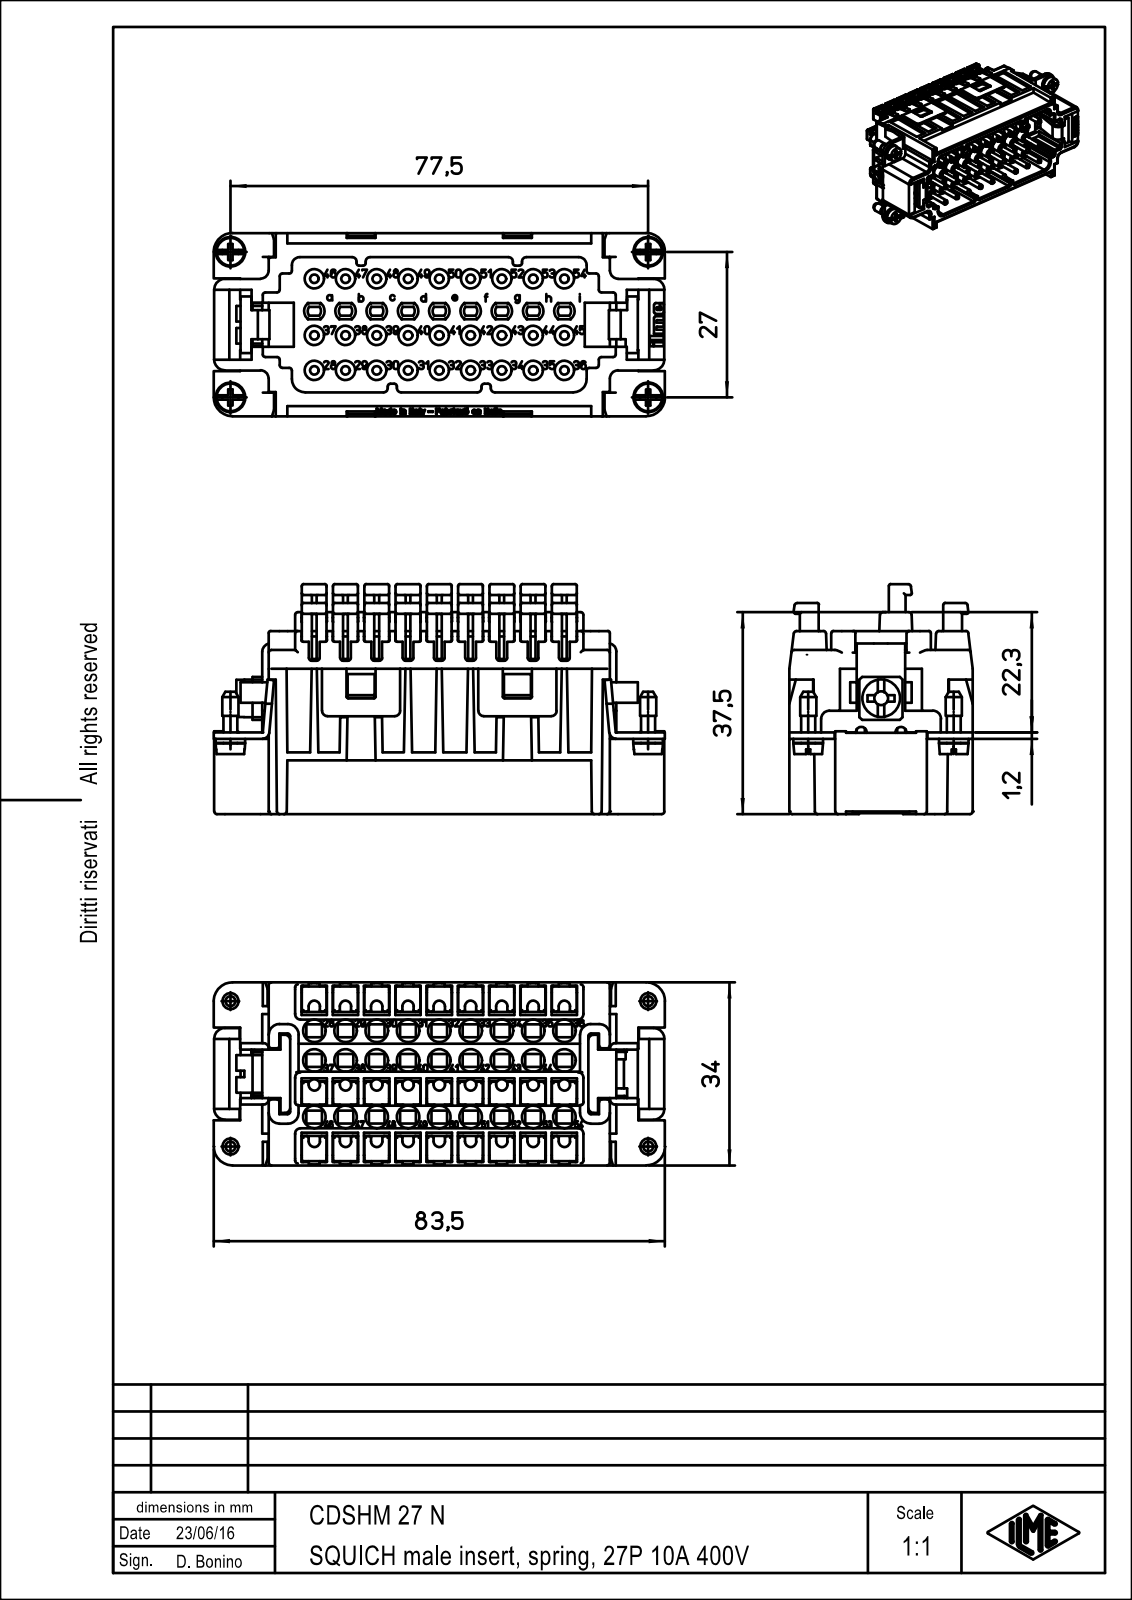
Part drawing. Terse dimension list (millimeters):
name: CDSHM_27_N
written by: PTC Creo Elements/Direct Modeling 19.0B 21-Mar-2015 (C) Parametric Technology GmbH (AUTOMOTIVE_DESIGN)
unit: mm
bodies: 1 solid, 2230 faces (1628 planar, 342 cylindrical, 260 other)
size: 84.36 × 46.84 × 34
volume: 53 399 mm³; area: 33 909 mm²
holes: 27× ⌀4.2, 1× ⌀4
bosses: 27× ⌀1.6, 4× ⌀5.5, 4× ⌀3, 1× ⌀7
rounds: 41× R0.5, 27× R1.05, 16× R1, 14× R2, 12× R1.5, 9× R1.1, 9× R1.25, 9× R1.9
face distances: 5.8, 4.6, 1.2, 11.6, 17.4, 0.9, 33.1, 7, 3.5, 10.1
hole spacings: 5.8, 7.99, 17.02, 11.6, 12, 19.76, 12.84, 15.65
